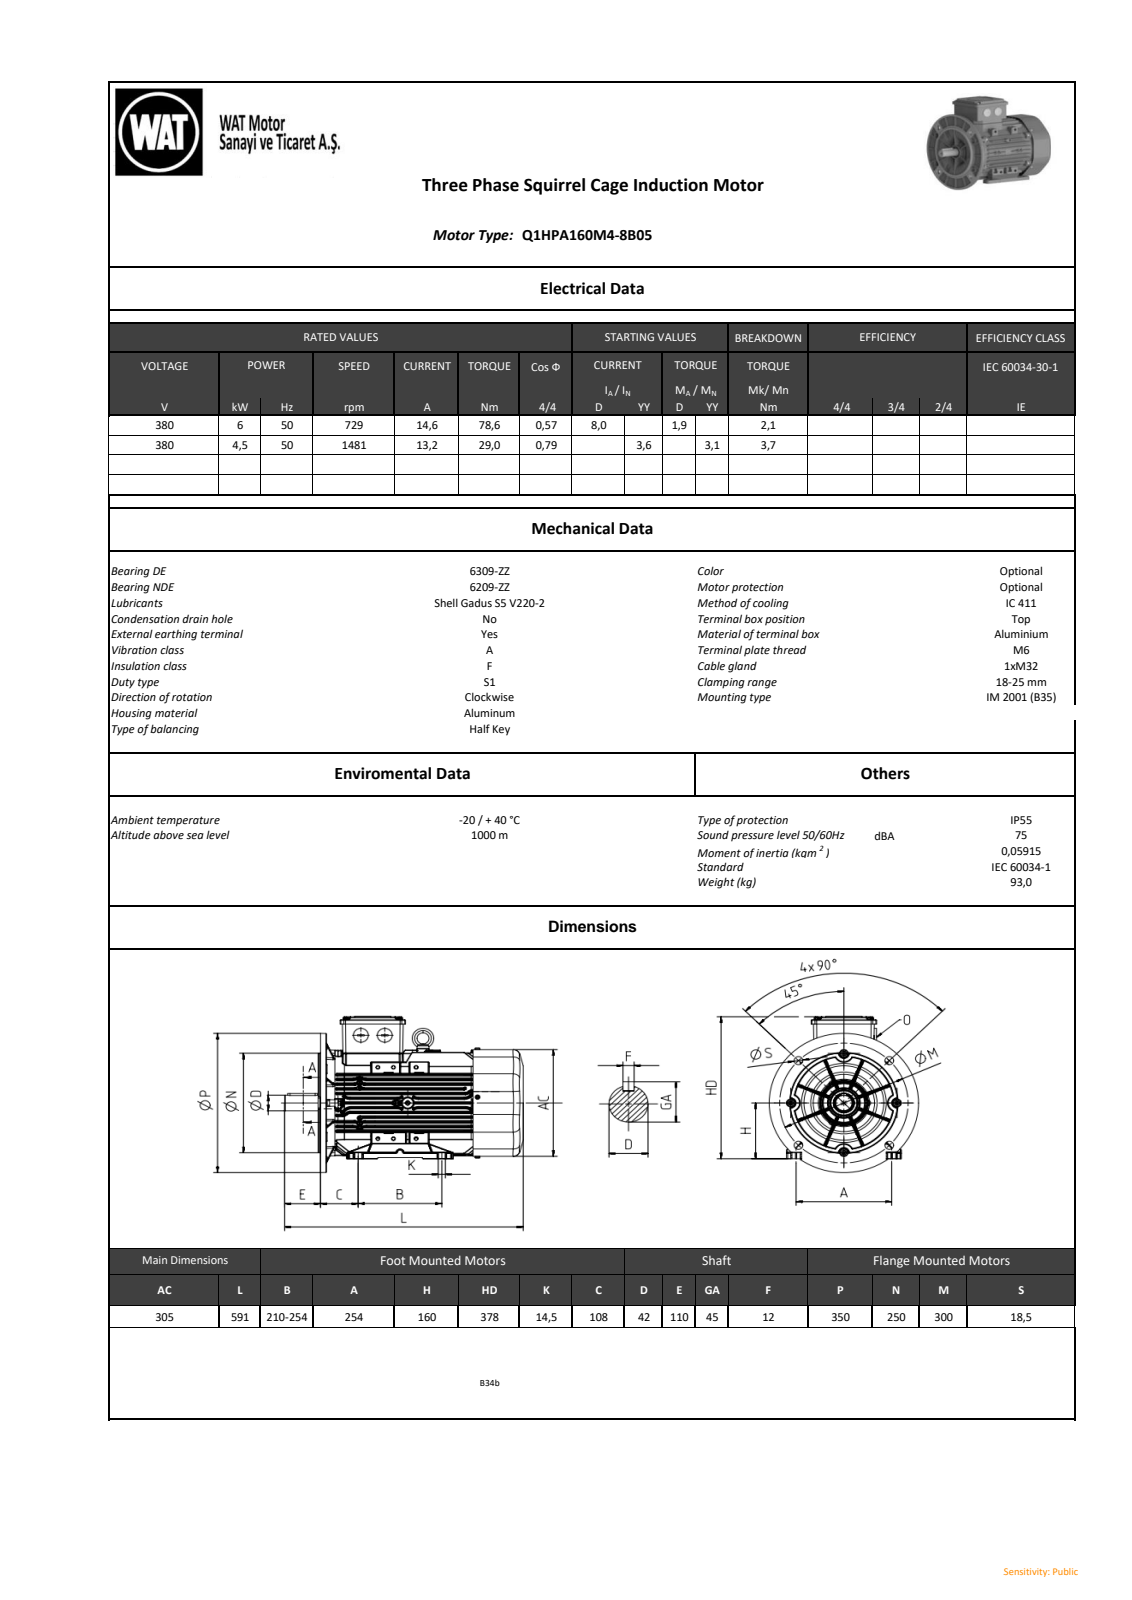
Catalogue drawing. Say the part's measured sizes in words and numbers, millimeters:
The part is named "QH series_ 160_B35_stp_objects". Its 3-D file was written by "SIEMENS PLM Software NX2206.8101 (AP203_CONFIGURATION_CONTROLLED_3D_DESIGN_OF_MECHANICAL_PARTS_AND_ASSEMBLIES_MIM_LF)". It is 0 solids with 8171 faces: 1987 planar, 3436 cylindrical and 2748 other. Overall it measures 590.5 by 392.75 by 350 millimeters. Round holes: 4 of diameter 16.5, 1 of diameter 10, 1 of diameter 14, 1 of diameter 17, 1 of diameter 72, 1 of diameter 85.63, 1 of diameter 94, 1 of diameter 114, 1 of diameter 134, 1 of diameter 154, 1 of diameter 174, 1 of diameter 194. Round bosses or shafts: 4 of diameter 16, 4 of diameter 10, 4 of diameter 8, 2 of diameter 38, 1 of diameter 272.5, 1 of diameter 250, 1 of diameter 178, 1 of diameter 158. Partial cylindrical surfaces (rounded edges, fillets, slot ends): 720 of radius 1, 625 of radius 0.5, 225 of radius 2, 129 of radius 4, 64 of radius 2.5, 56 of radius 5, 34 of radius 6, 33 of radius 3. The main face-to-face distances are 168, 144, 11.92, 9.62, 14.77, 168.39, 158.77, 24.39, 120, 11.85. The hole center spacings are 142.5, 201.53, 142.31, 142.34, 142.66, 142.69, 285, 142.3.
